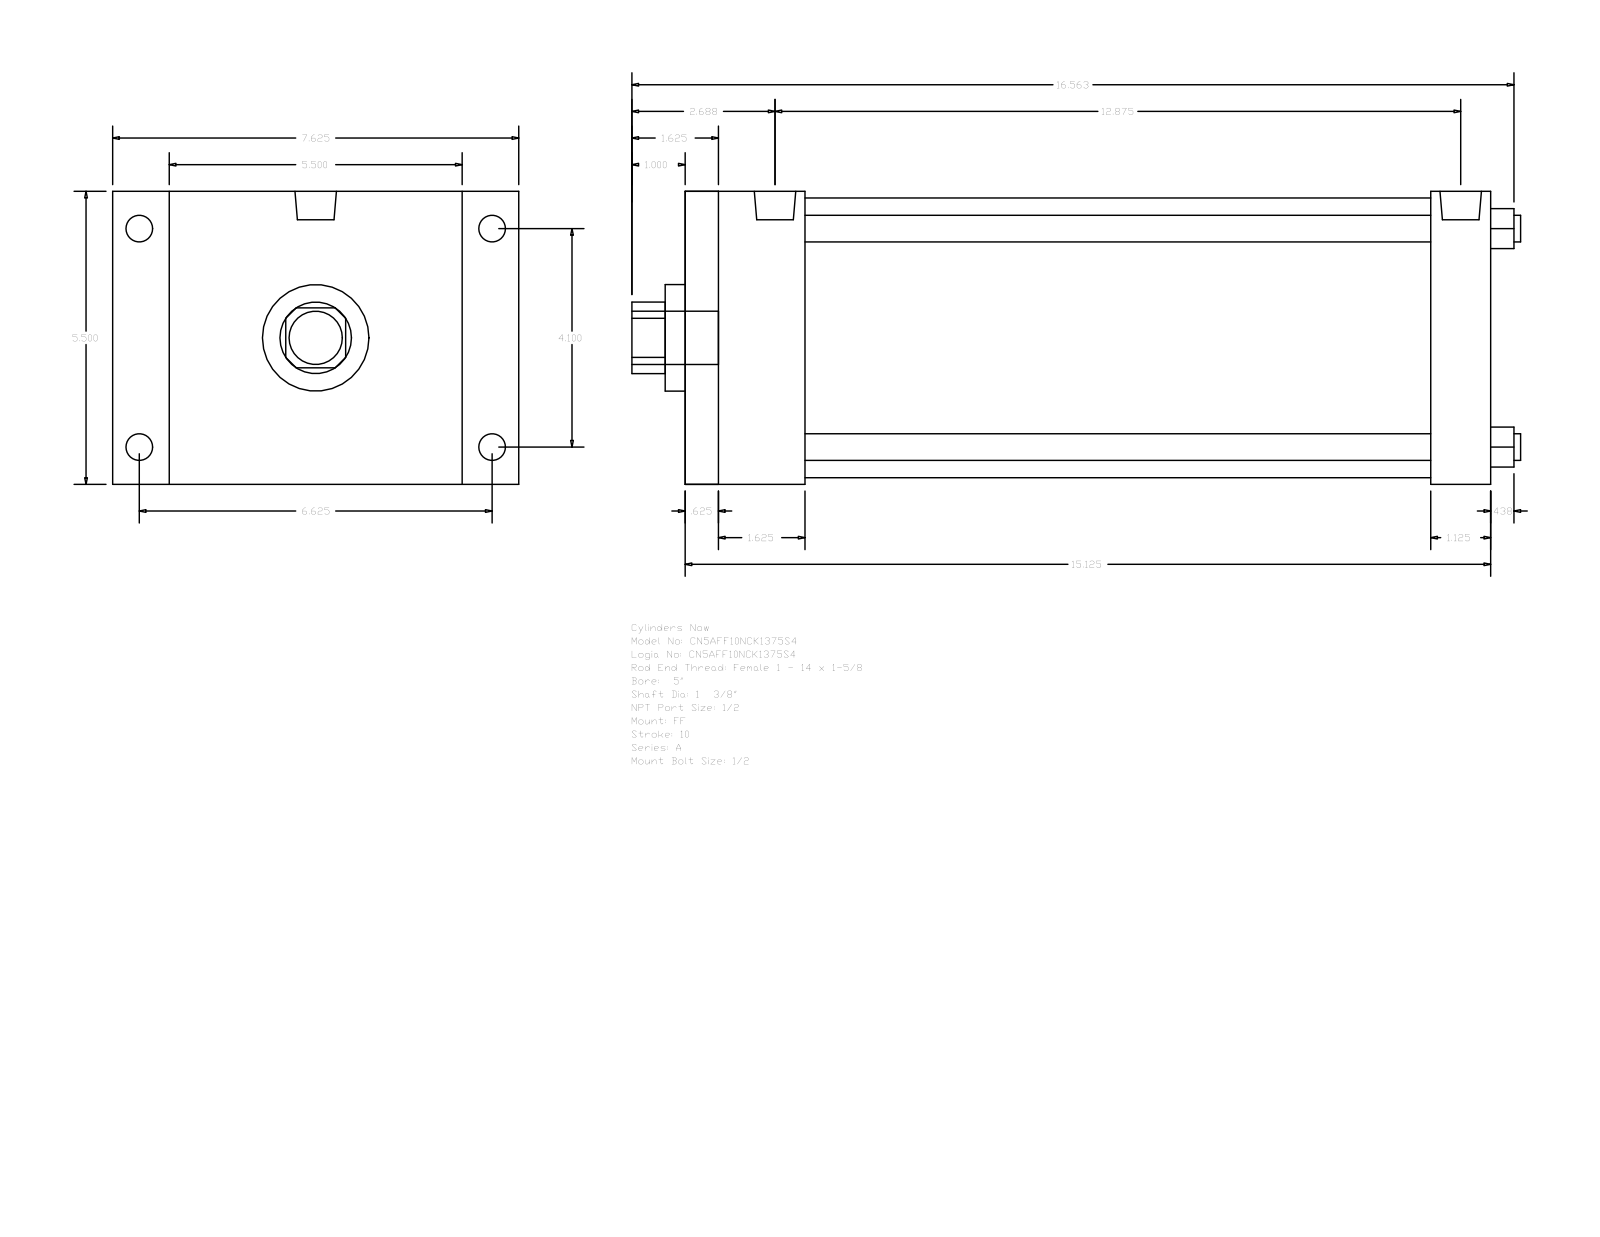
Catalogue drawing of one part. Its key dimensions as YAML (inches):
part_name: "A_FF__0500_1.375"
step_written_by: "GSSL Pune (CONFIG_CONTROL_DESIGN)"
units: inches
bodies: {solids: 0, faces: 92, planar: 64, cylindrical: 28, other: 0}
overall_size: [16.687, 7.625, 5.5]
round_holes:
  - {diameter: 0.5, count: 4}
  - {diameter: 1.375, count: 1}
  - {diameter: 2, count: 1}
  - {diameter: 5.25, count: 1}
round_bosses_or_shafts:
  - {diameter: 0.5, count: 4}
  - {diameter: 0.344, count: 4}
  - {diameter: 0.778, count: 2}
  - {diameter: 1, count: 1}
partial_cylinders:
  - {radius: 0.672, count: 1}
face_to_face_distances: [5.5, 15.125, 14.5, 0.625, 1.125, 14, 13.375, 2.25, 1.625, 11.75]
hole_center_spacings: [2.899, 4.1, 5.798]
